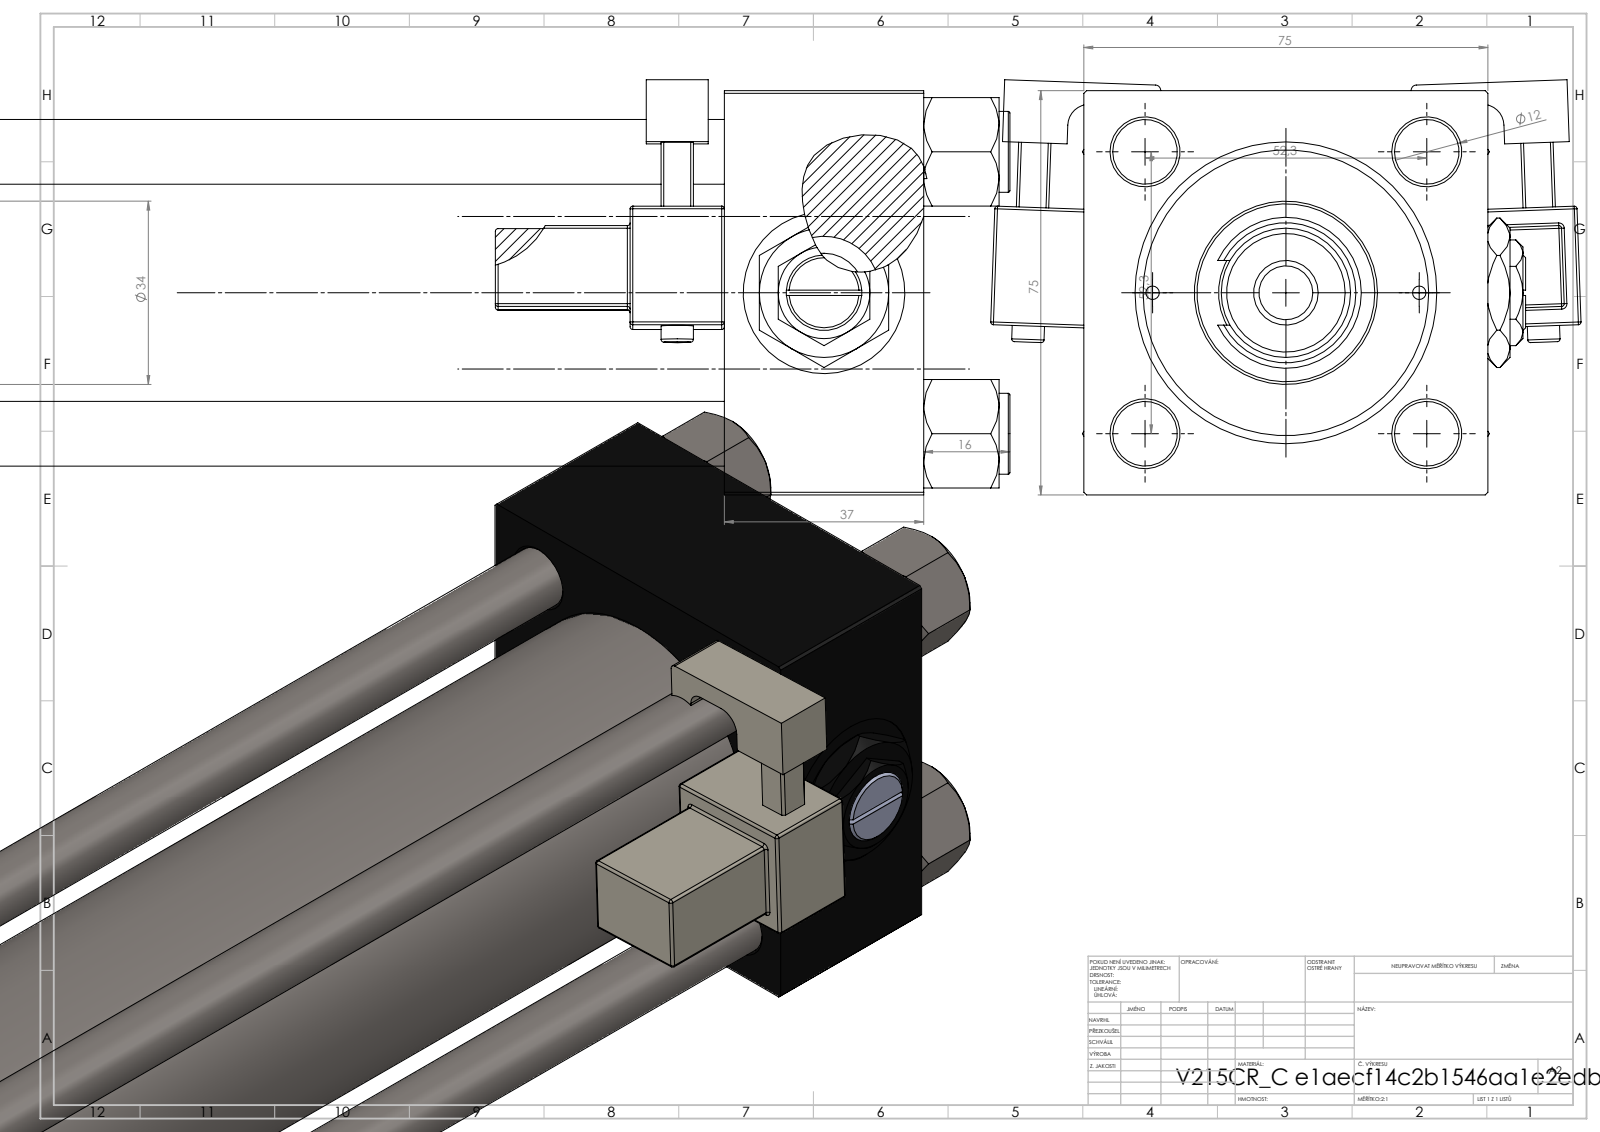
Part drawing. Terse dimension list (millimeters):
name: NUT_M5_C; V215CR_C_Body; FEMALE_PART_FOR_DFA; V215_VC_A (+5 more)
written by: SolidWorks 2019 (CONFIG_CONTROL_DESIGN)
unit: mm
bodies: 17 solids, 1494 faces (661 planar, 175 cylindrical, 658 other)
size: 836 × 109.57 × 77.03
volume: 1 483 000 mm³; area: 491 925 mm²
holes: 4× ⌀12, 2× ⌀2.5, 2× ⌀7, 2× ⌀20.96, 2× ⌀30, 1× ⌀10.5, 1× ⌀22, 1× ⌀25, 1× ⌀41, 1× ⌀50, 1× ⌀53
bosses: 4× ⌀15, 2× ⌀6, 1× ⌀56, 1× ⌀34, 1× ⌀28, 1× ⌀24, 1× ⌀18, 1× ⌀12
rounds: 48× R0.5, 2× R1, 2× R2.5, 2× R4, 1× R9.75, 1× R10.5
face distances: 75, 37, 734, 697, 675, 638, 59, 705.3, 668.3, 30.3
hole spacings: 26.19, 36.98, 52.3, 57.22, 24.75, 73.96, 49.5, 673.5
